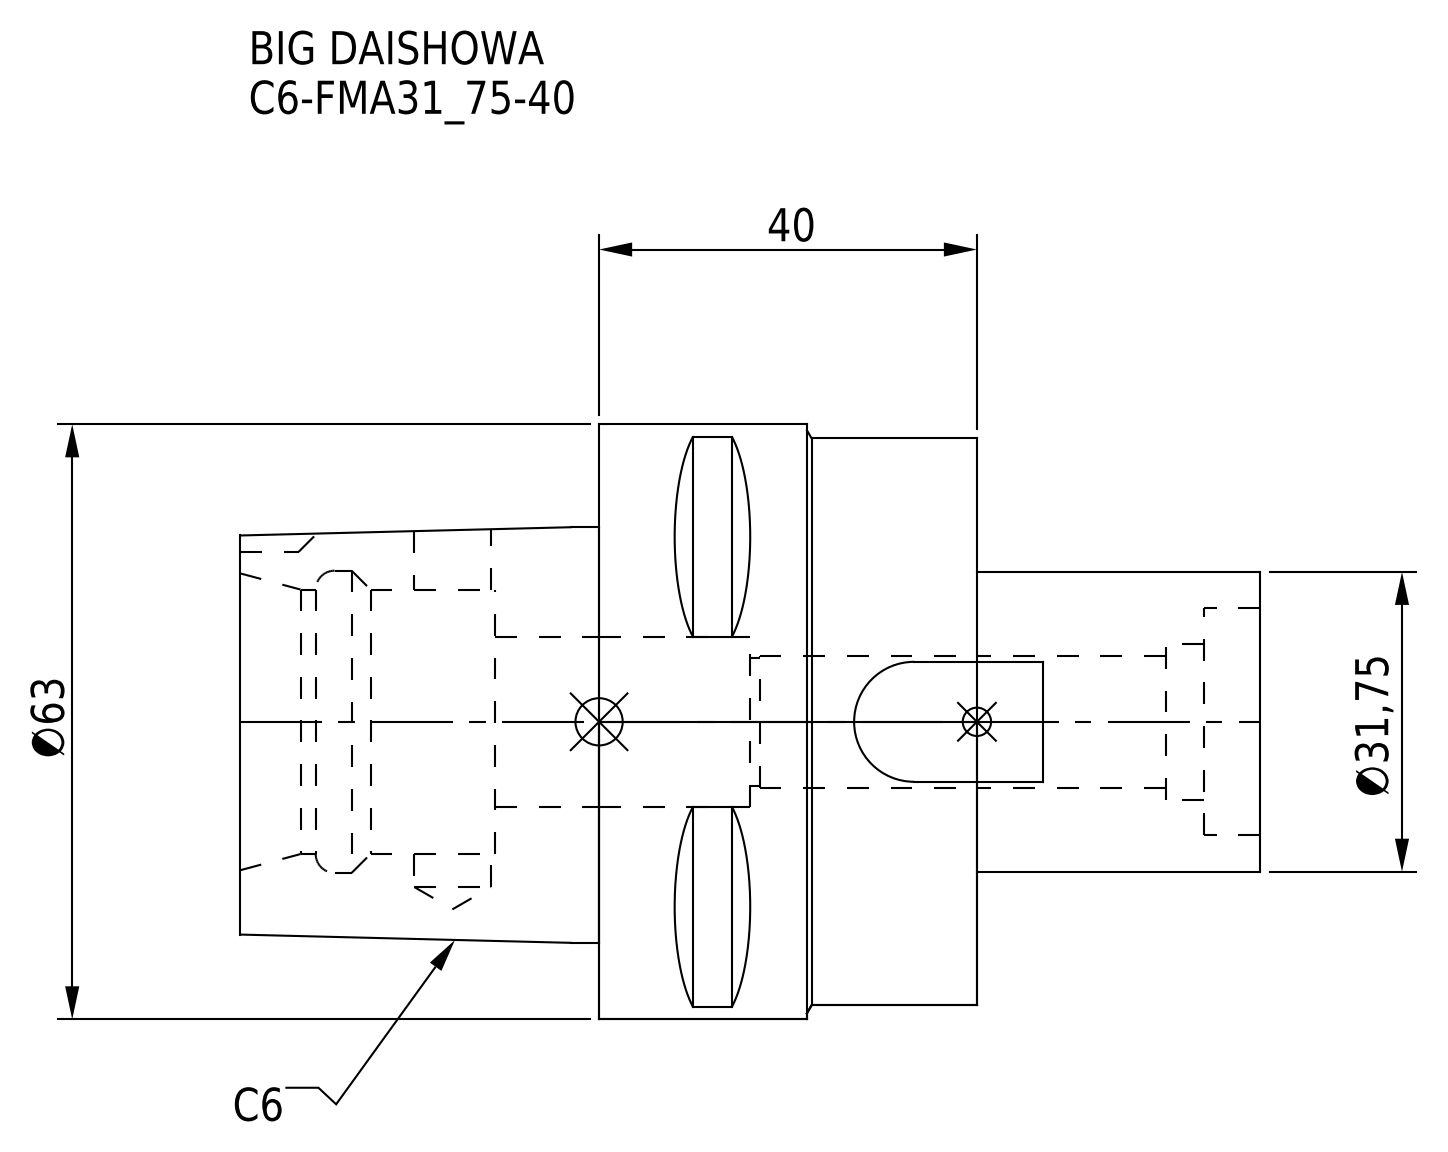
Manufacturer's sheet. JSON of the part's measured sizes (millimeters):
{"part_name": "C6-FMA31_75-40", "step_written_by": "CREO PARAMETRIC BY PTC INC, 2016380 (AUTOMOTIVE_DESIGN)", "units": "millimeters", "bodies": {"solids": 1, "faces": 81, "planar": 42, "cylindrical": 27, "other": 12}, "overall_size": [108, 63, 63], "volume_mm3": 162896, "surface_area_mm2": 29437, "round_holes": [[8.1, 1], [13.5, 1], [14, 1], [16.5, 1], [18, 1], [24, 1], [28, 1], [32, 1]], "round_bosses_or_shafts": [[63, 1], [60, 1], [31.75, 1]], "partial_cylinders_radius": [[5, 1]], "face_to_face_distances": [40, 38, 11, 78, 27, 47, 58, 51, 30, 6]}
